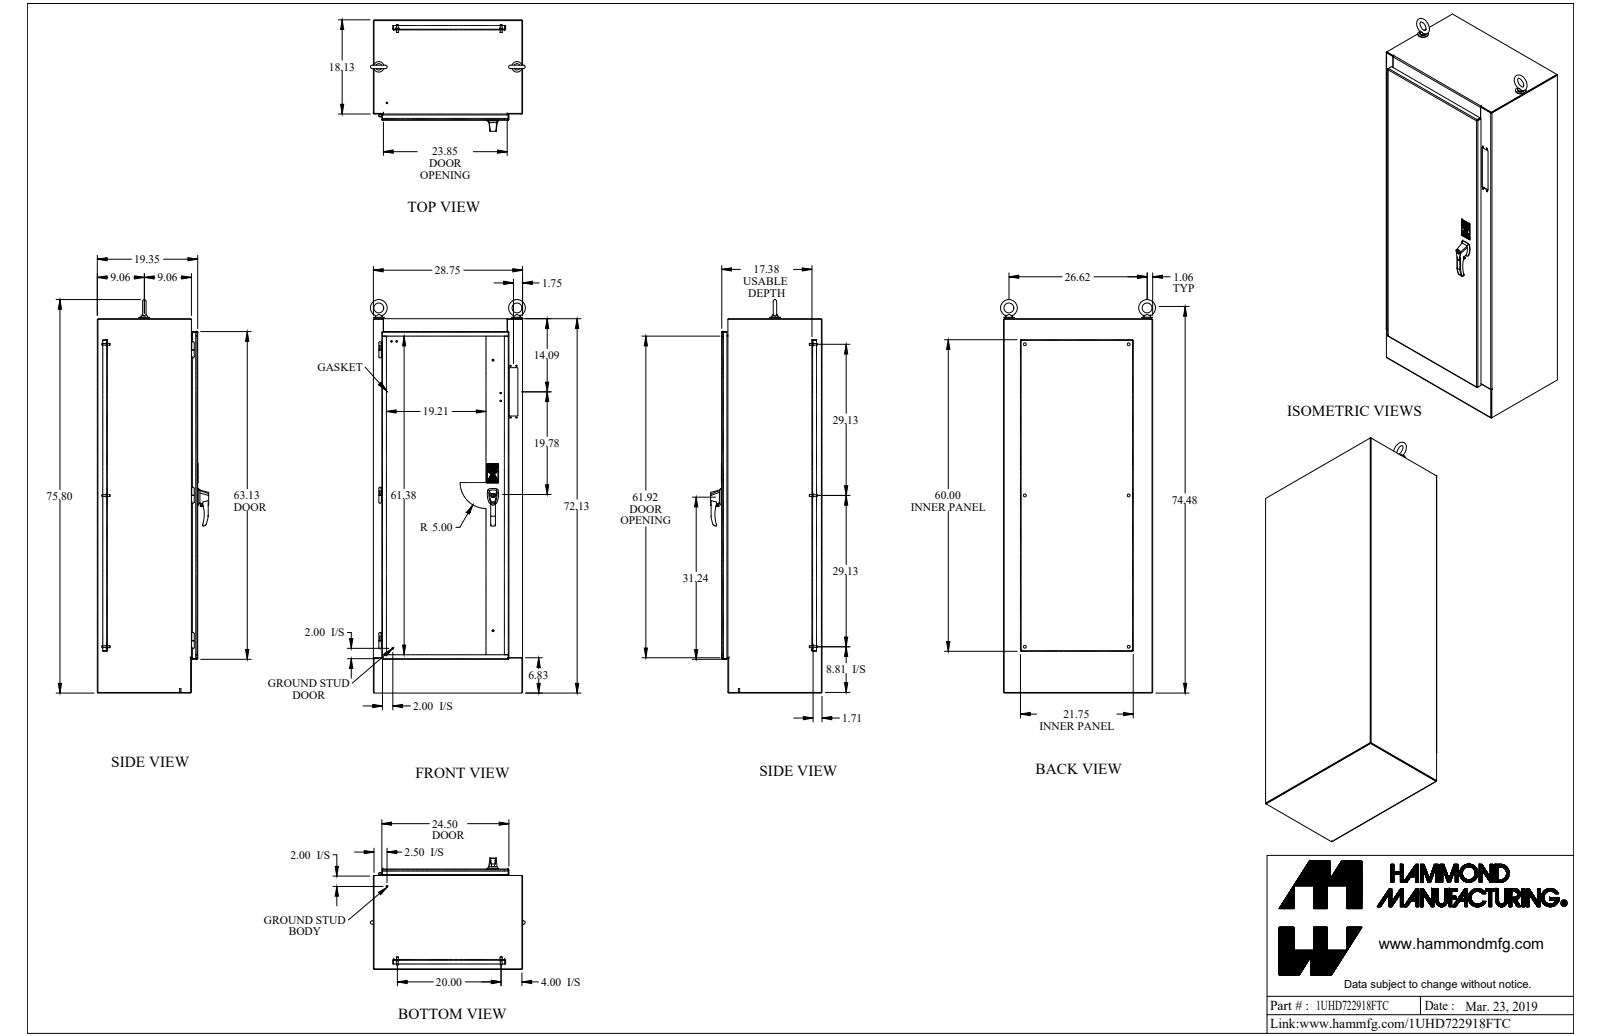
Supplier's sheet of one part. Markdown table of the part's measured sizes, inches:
| quantity | value |
| --- | --- |
| part name | 1UHD722918FTC |
| STEP written by | SolidWorks 2018 (AUTOMOTIVE_DESIGN) |
| units | inches |
| bodies | 102 solids, 1773 faces (978 planar, 482 cylindrical, 313 other) |
| overall size | 75.799 × 29.872 × 21.464 |
| volume | 1 376 in³ |
| surface area | 22 002 in² |
| round holes (diameter × count) | 0.307 × 7, 0.35 × 7, 0.281 × 6, 0.445 × 6, 0.563 × 6, 0.196 × 5, 0.25 × 3, 0.313 × 3, 0.167 × 2, 0.255 × 2, 0.257 × 2, 0.28 × 2 |
| round bosses / shafts (diameter × count) | 0.25 × 10, 1 × 8, 0.65 × 6, 0.375 × 6, 0.33 × 6, 0.281 × 4, 0.188 × 4, 0.625 × 3 |
| partial cylindrical surfaces (radius × count) | 0.06 × 39, 0.185 × 28, 0.5 × 25, 0.125 × 22, 0.017 × 16, 0.032 × 12, 0.13 × 8, 0.75 × 7 |
| main face-to-face distances | 0.125, 0.125, 17.413, 19.225, 19.1, 19.35, 19.224, 28.5, 28.625, 28.625 |
| hole center spacings | 20, 1, 1.125, 1.126, 1.287, 2, 7.5, 9.936 |
